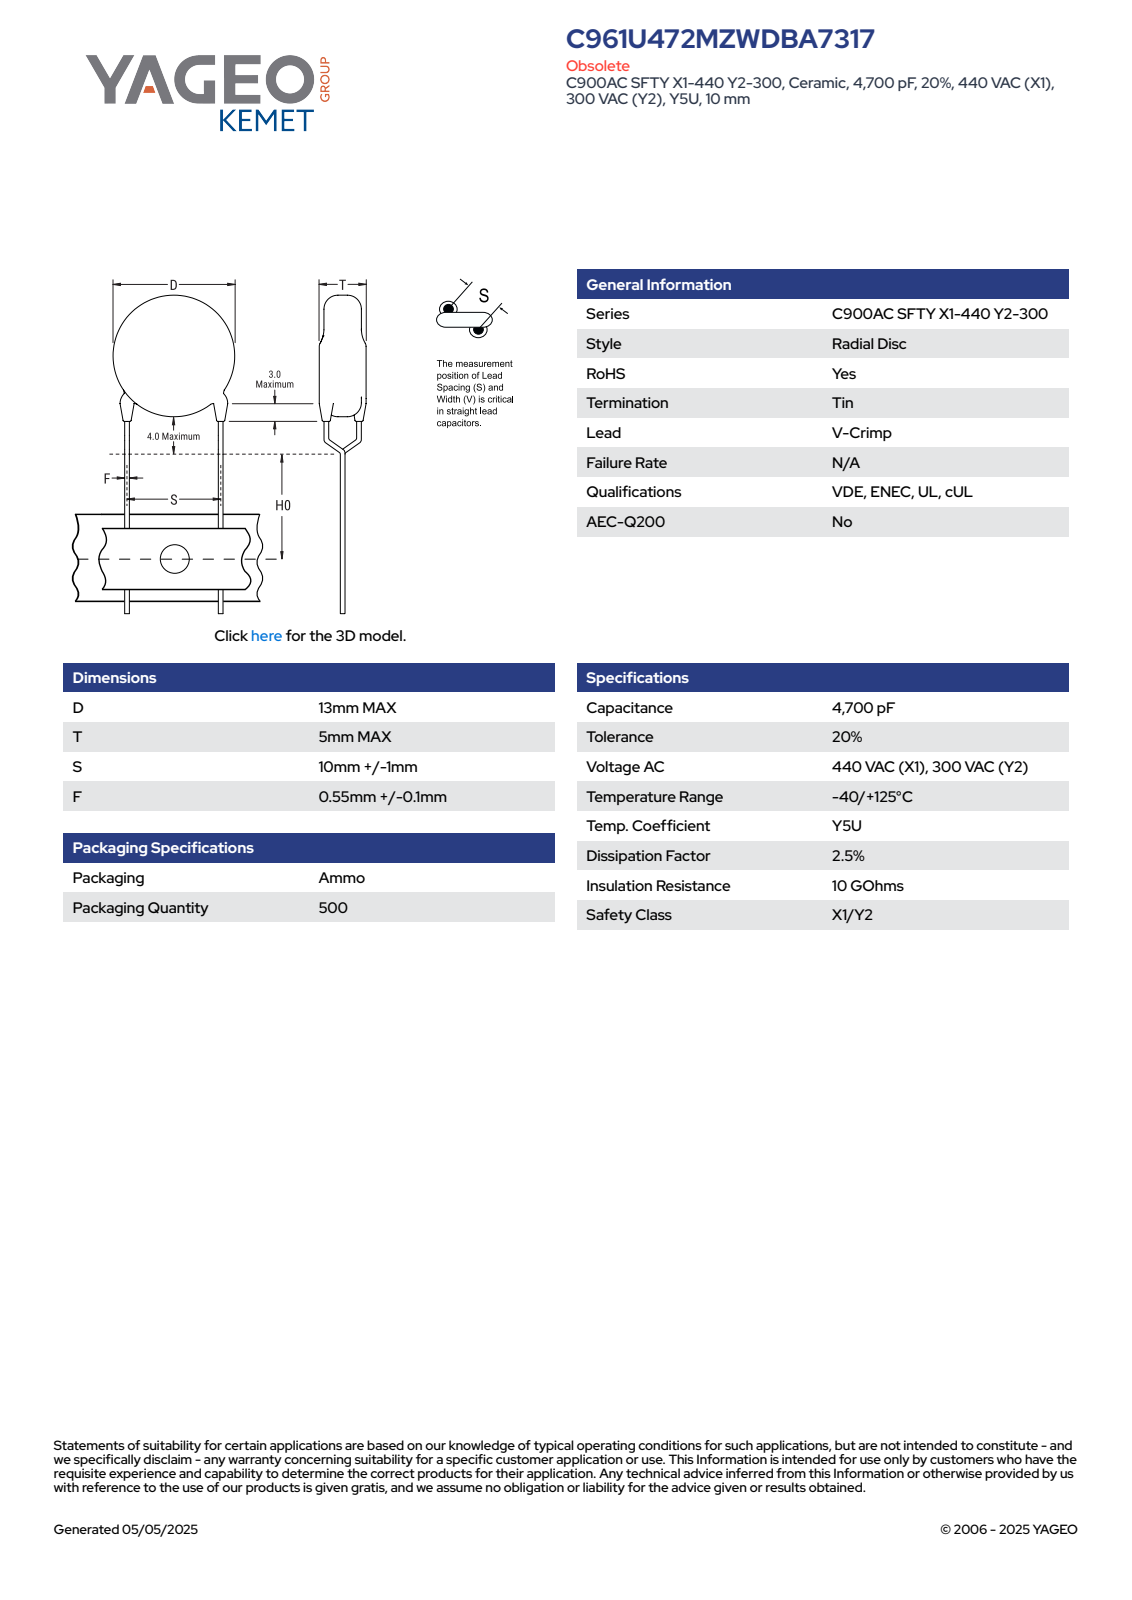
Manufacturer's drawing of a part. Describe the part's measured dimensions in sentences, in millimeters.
The part is named "CCD_VCC900_D13T5S10LL20F0.65". Its 3-D file was written by "SolidWorks 2014 (AUTOMOTIVE_DESIGN)". It is 5 solids with 93 faces: 65 planar, 16 cylindrical and 12 other. Overall it measures 36.8 by 13 by 5 millimeters. Its volume is 666 cubic millimeters and its surface area 561 square millimeters. Round bosses or shafts: 6 of diameter 0.65, 1 of diameter 13. The main face-to-face distances are 5, 22.9, 31.14, 8.24, 29.45, 6.55, 1.69, 0.46, 6.9, 0.63.
